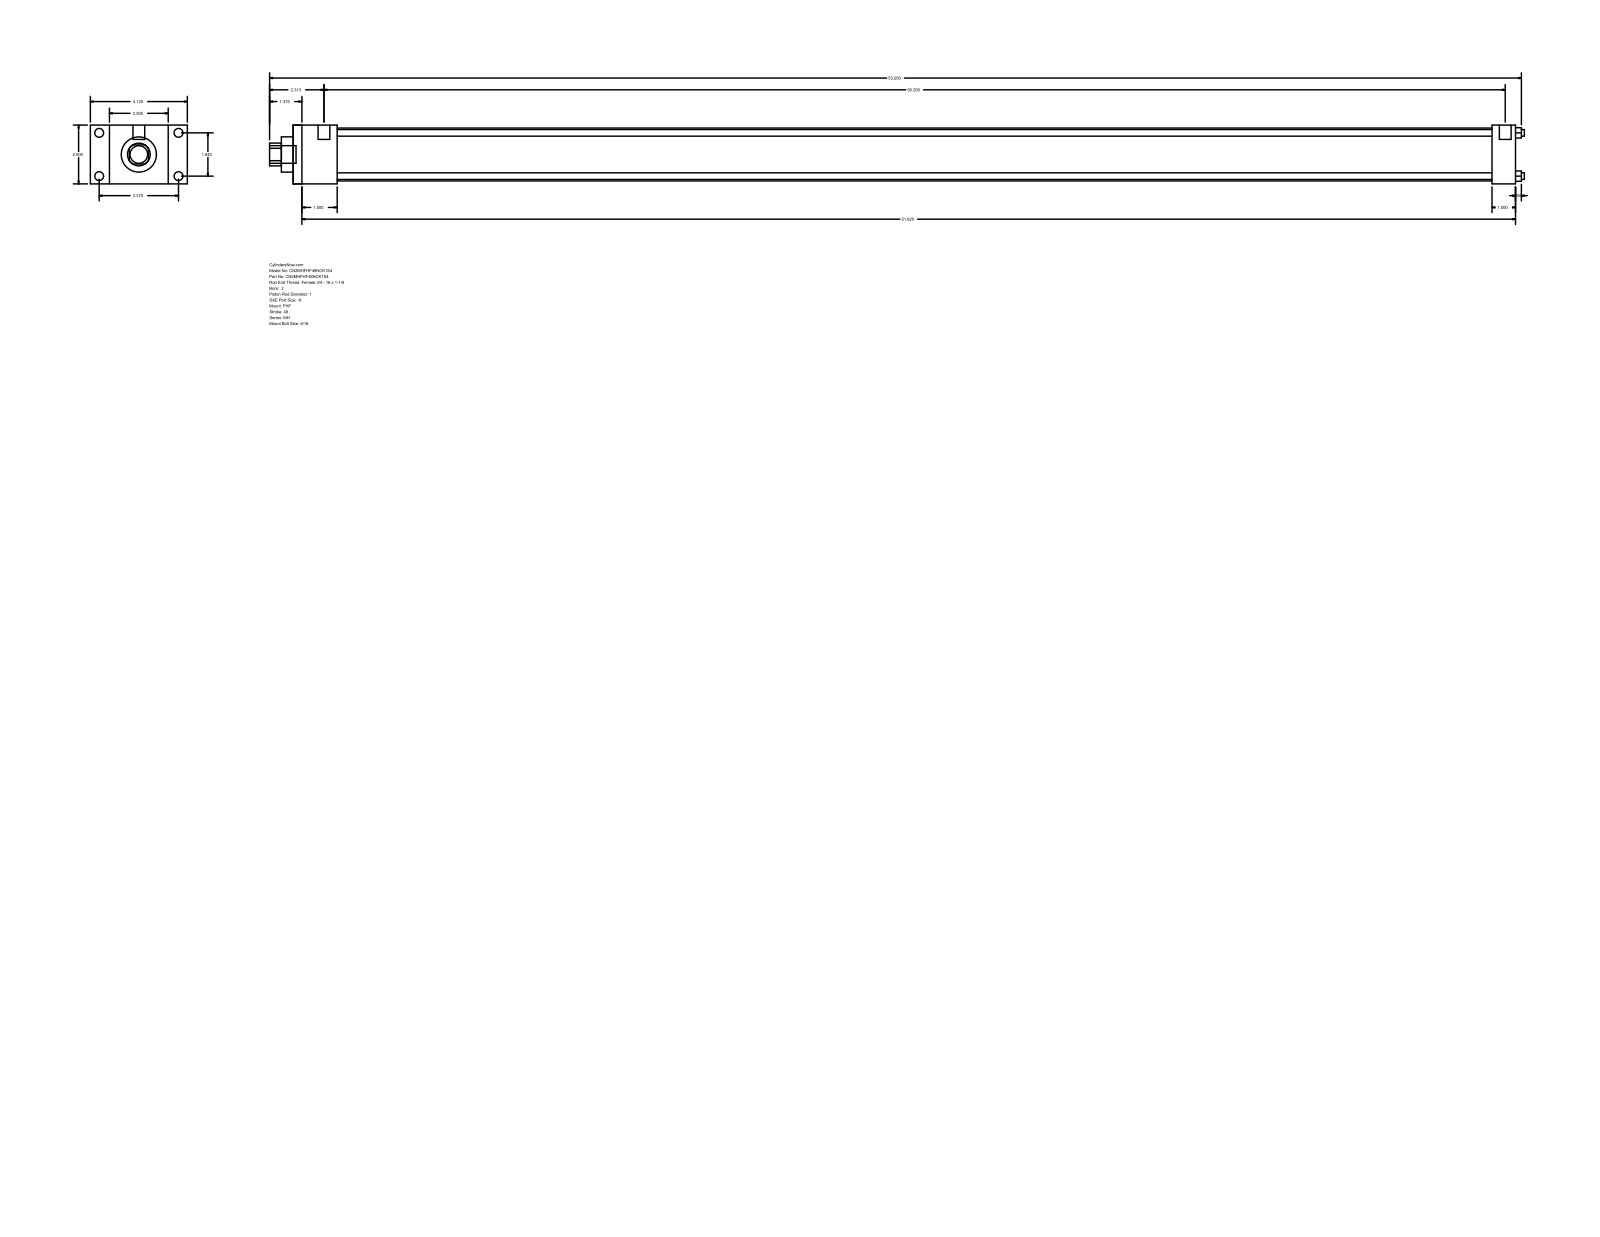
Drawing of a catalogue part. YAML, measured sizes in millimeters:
part_name: "MH_FHF__0200_1"
step_written_by: "GSSL Pune (CONFIG_CONTROL_DESIGN)"
units: millimeters
bodies: {solids: 0, faces: 88, planar: 60, cylindrical: 28, other: 0}
overall_size: [1355.72, 104.78, 63.5]
round_holes:
  - {diameter: 7.14, count: 4}
  - {diameter: 25.4, count: 1}
  - {diameter: 38.1, count: 1}
  - {diameter: 57.15, count: 1}
round_bosses_or_shafts:
  - {diameter: 9.53, count: 4}
  - {diameter: 5.56, count: 4}
  - {diameter: 12.7, count: 2}
  - {diameter: 19.05, count: 1}
partial_cylinders:
  - {radius: 12.29, count: 1}
face_to_face_distances: [63.5, 1320.8, 47.63, 1273.17, 20.64, 84.14, 104.78, 25.4, 1295.4, 1247.77]
hole_center_spacings: [33.05, 46.74, 66.1]
